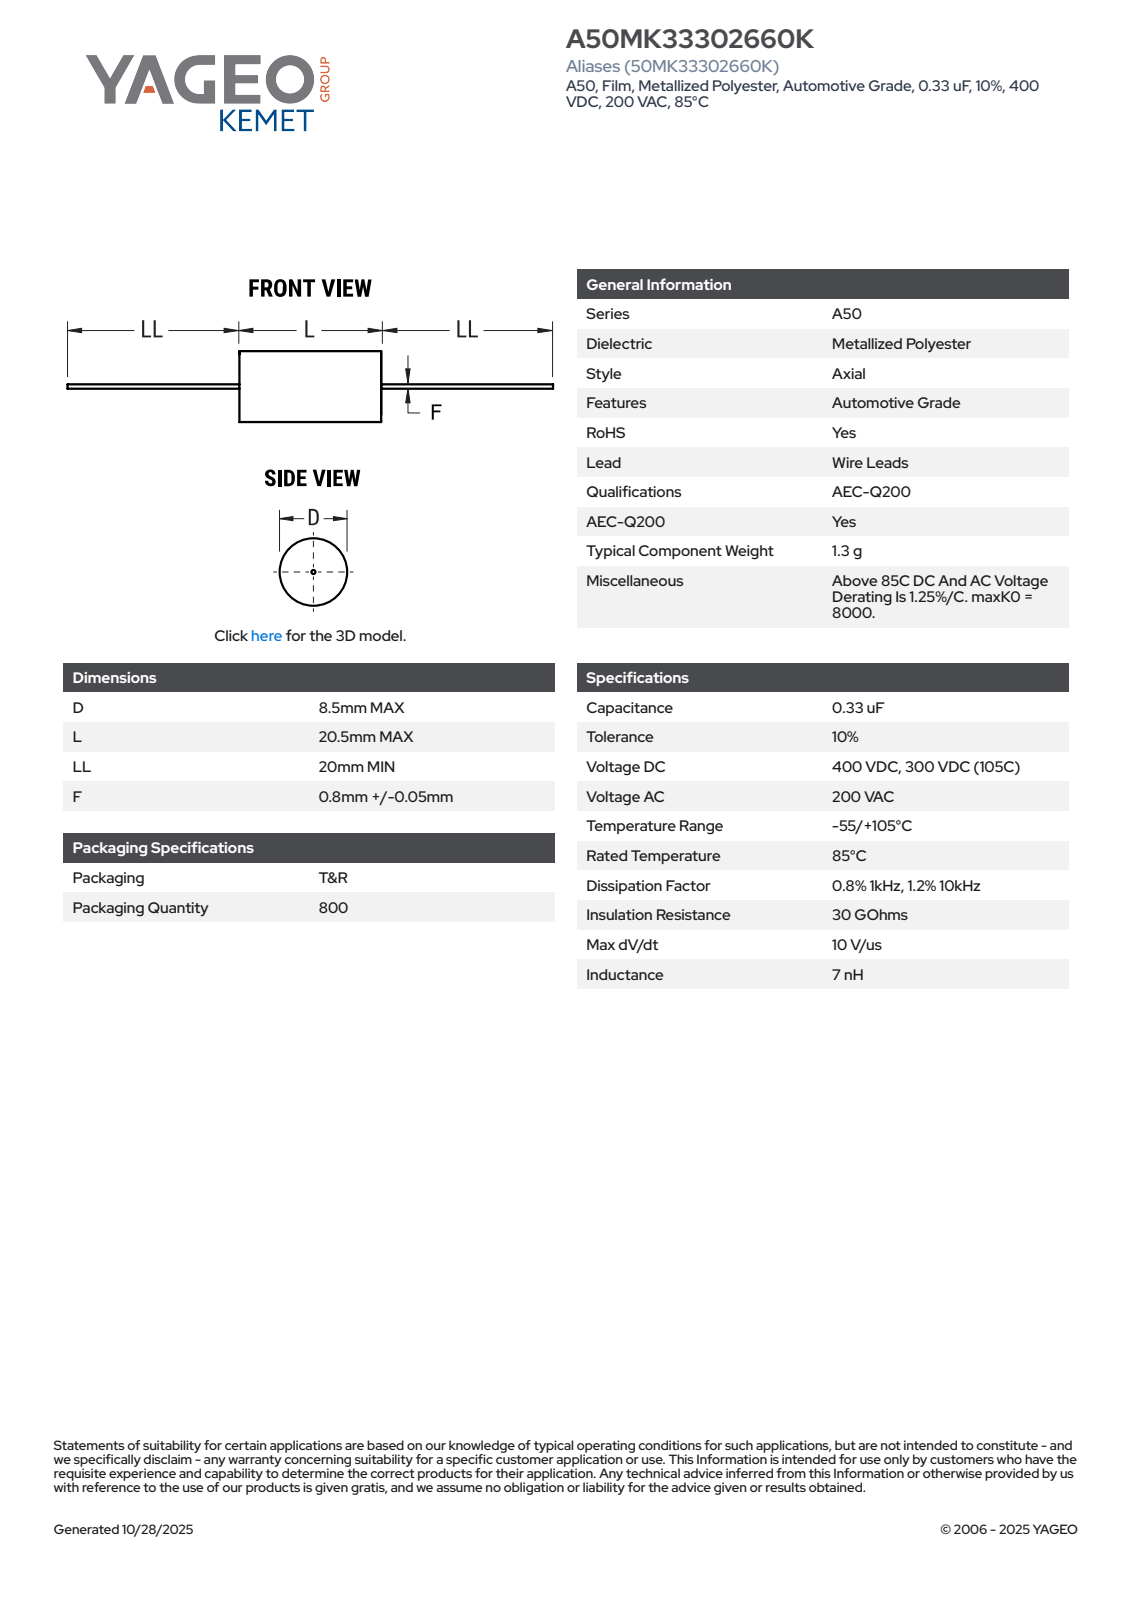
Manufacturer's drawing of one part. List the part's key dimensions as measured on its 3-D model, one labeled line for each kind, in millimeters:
Part name (STEP PRODUCT): CFA_ACWF_8.5X20.5_D8.5L20.5LL38F0.85
STEP written by: SolidWorks 2014 (AUTOMOTIVE_DESIGN)
Units: millimetres
Bodies: 1 solid, 72 faces (26 planar, 15 cylindrical, 31 other)
Overall size (bounding box): 96.5 × 8.51 × 8.5
Volume: 1 207 mm³ · Surface area: 864 mm²
Round bosses / shafts (diameter × count): ⌀8.5 ×1, ⌀0.85 ×1
Partial cylindrical surfaces — rounded edges, fillets, slot ends (radius × count): R4.26 ×1
Main face-to-face distances: 20.5, 38, 58.5, 96.5
